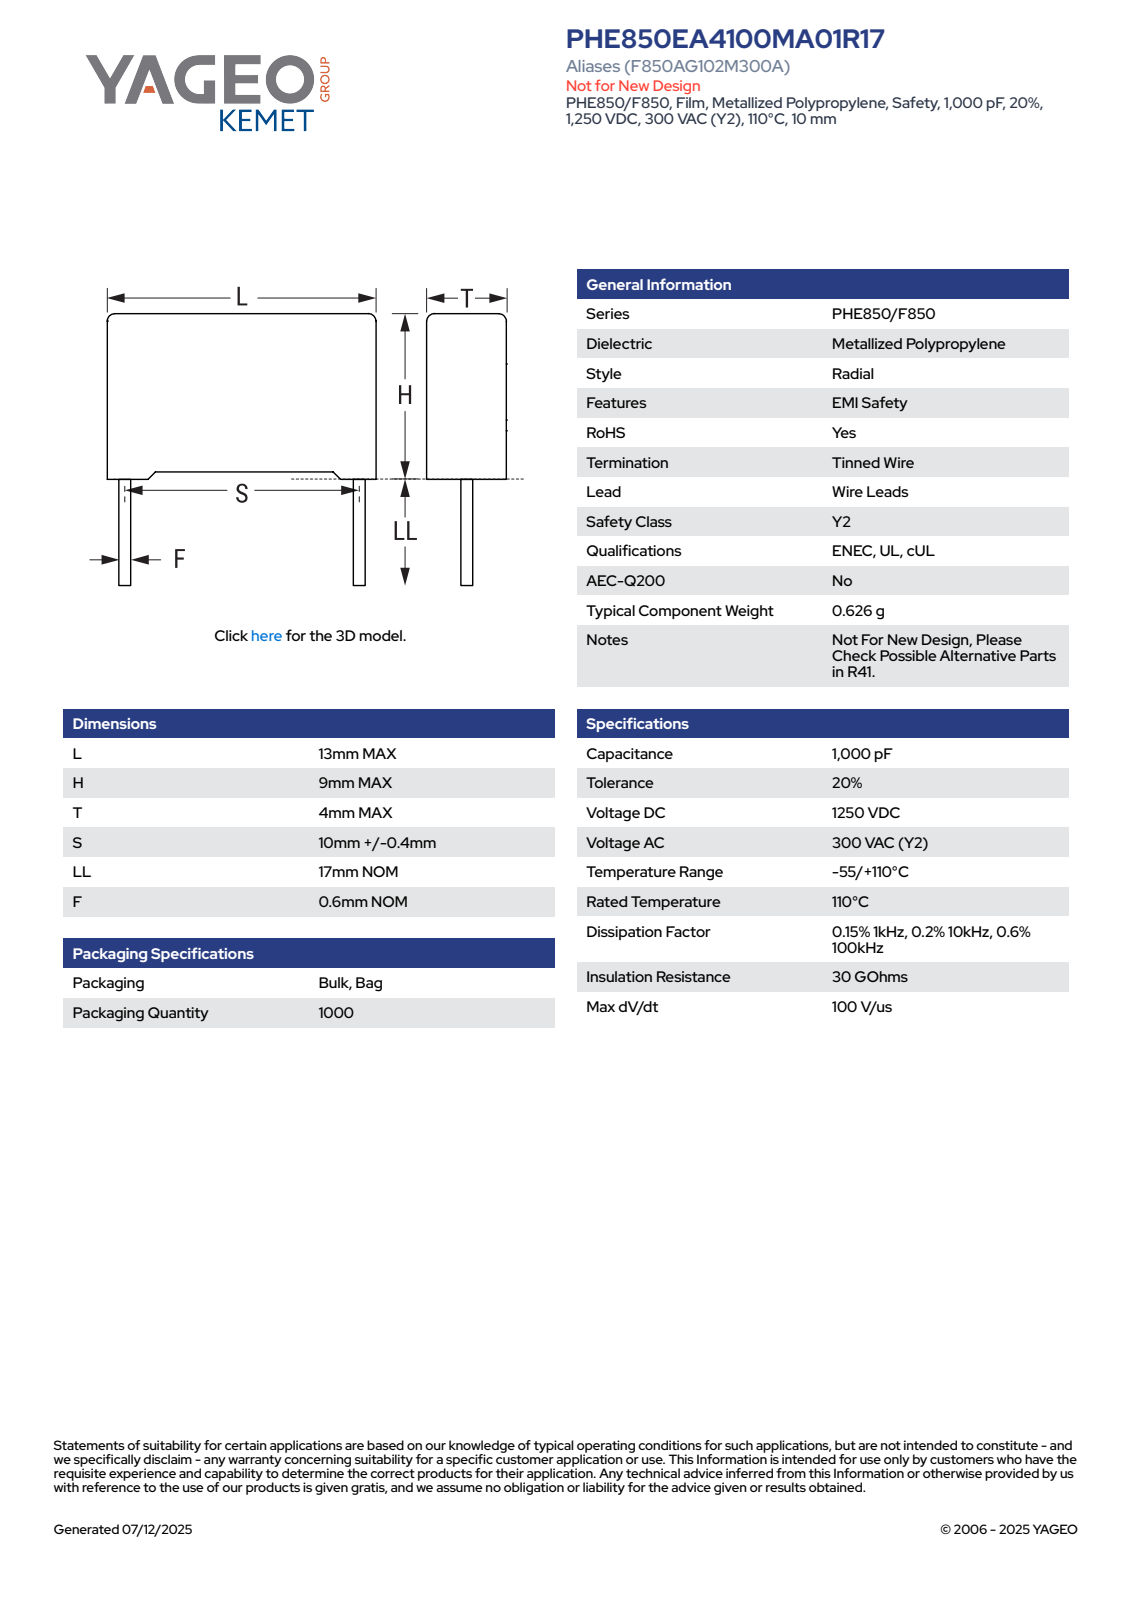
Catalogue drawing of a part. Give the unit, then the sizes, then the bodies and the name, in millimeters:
Units: millimetres
Overall size (bounding box): 26 × 13 × 4
Round bosses / shafts (diameter × count): ⌀0.6 ×2
Partial cylindrical surfaces — rounded edges, fillets, slot ends (radius × count): R0.5 ×4
Main face-to-face distances: 4, 8.25, 13, 0.43, 3.57, 0.75, 9, 3.14, 0.31, 0.44
Volume: 446 mm³ · Surface area: 497 mm²
Bodies: 4 solids, 85 faces (77 planar, 8 cylindrical, 0 other)
Part name (STEP PRODUCT): CFR_RB2_13X9X4_L13H9T4S10LL17F0.6
STEP written by: SolidWorks 2021 (AUTOMOTIVE_DESIGN)
